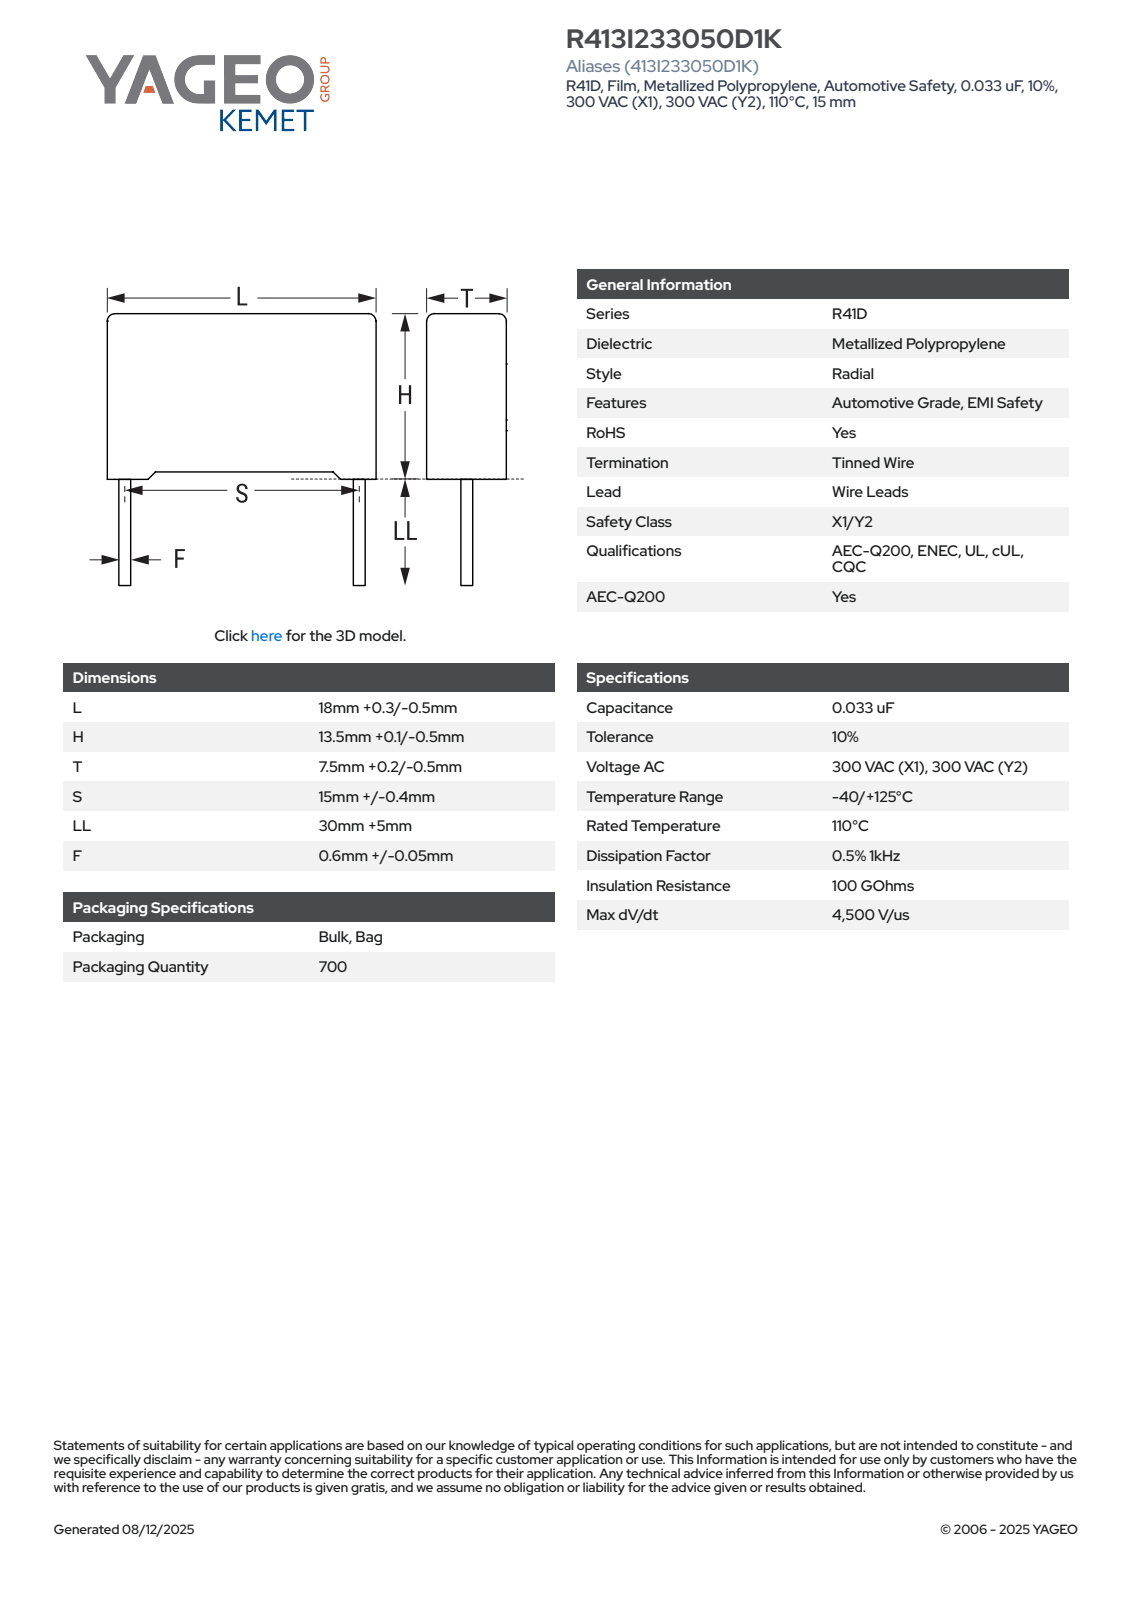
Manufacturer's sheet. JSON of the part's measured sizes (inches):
{"part_name": "CFR_RB2_18X13.5X7.5_L18.3H13.6T7.7S15LL35F0.65", "step_written_by": "SolidWorks 2021 (AUTOMOTIVE_DESIGN)", "units": "inches", "bodies": {"solids": 4, "faces": 85, "planar": 77, "cylindrical": 8, "other": 0}, "overall_size": [1.913, 0.72, 0.304], "volume_in3": 0.113, "surface_area_in2": 1.803, "round_bosses_or_shafts": [[0.026, 2]], "partial_cylinders_radius": [[0.02, 4]], "face_to_face_distances": [0.303, 0.506, 0.72, 0.024, 0.03, 0.535, 0.279, 0.019, 0.517, 0.696]}
